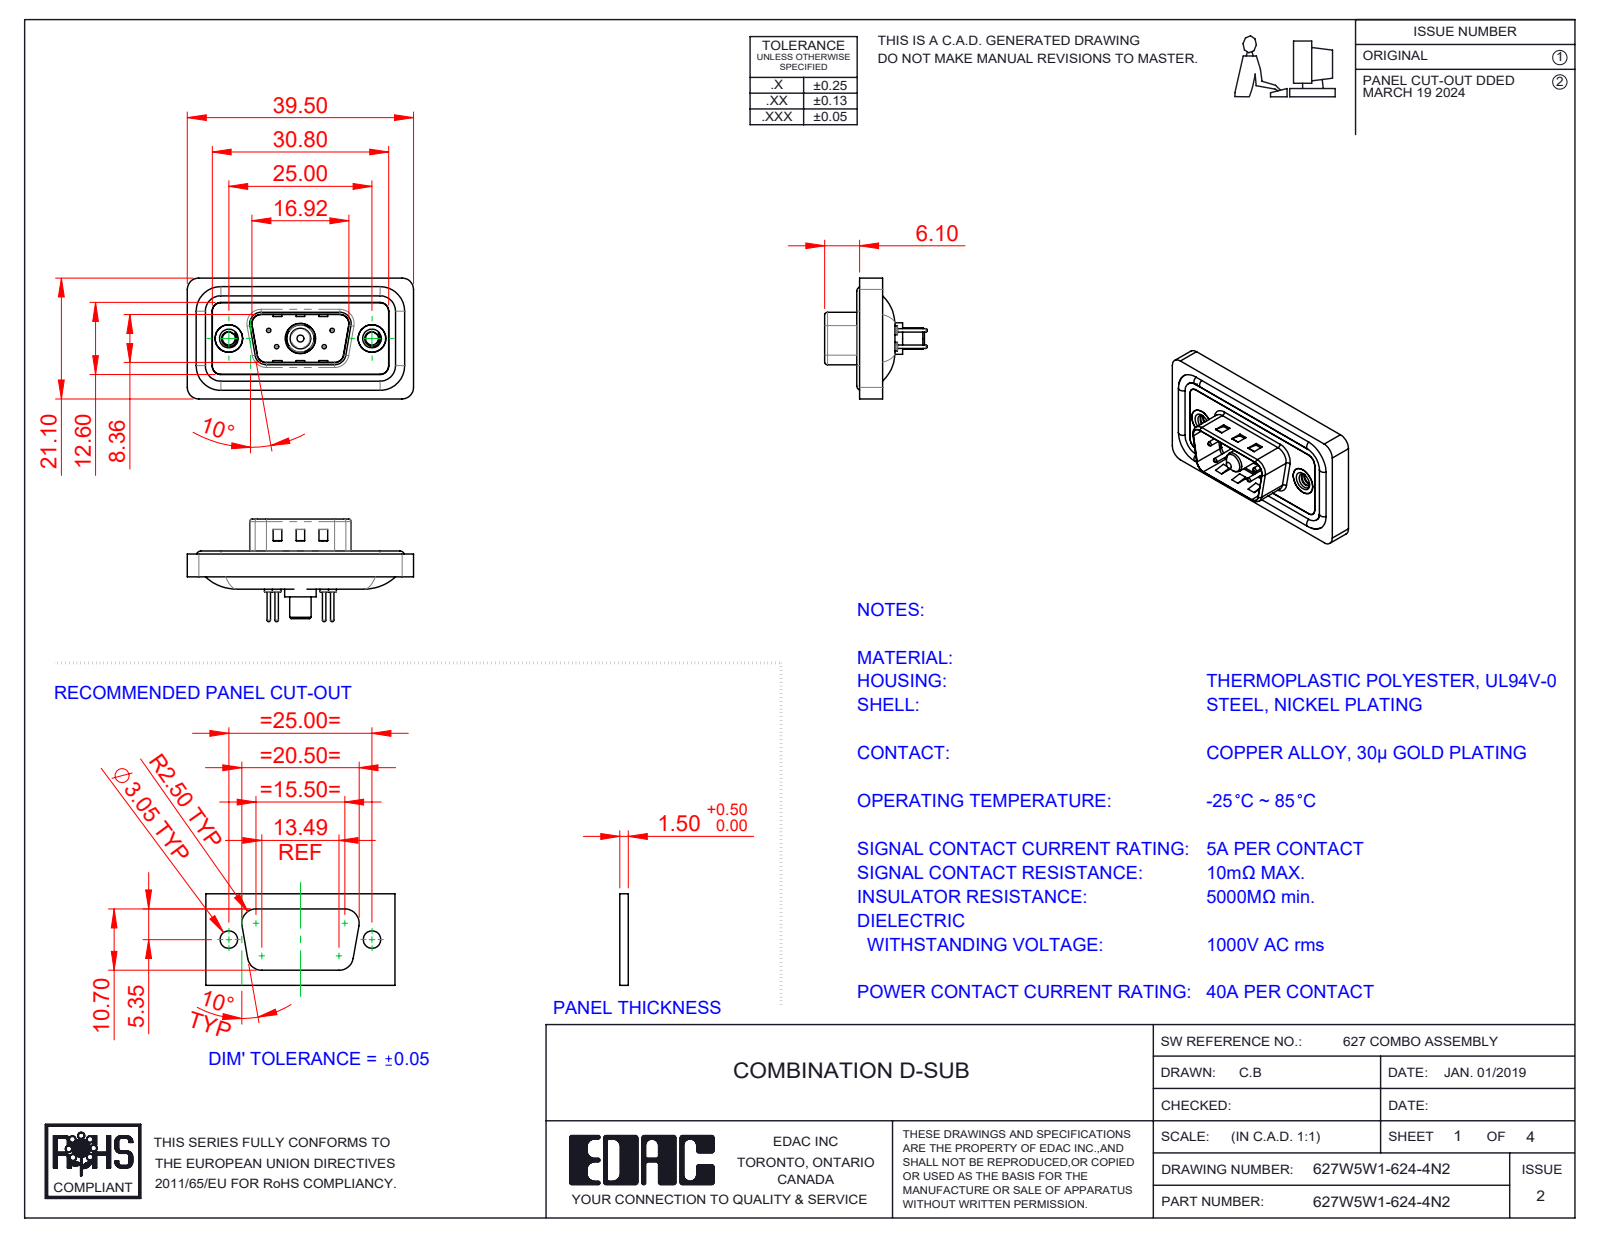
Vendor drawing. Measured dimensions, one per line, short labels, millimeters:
name: 627Combo Waterproof Housing_09 Contacts; 627W5W1-624-4N2; 627Combo Threaded Rivet_2; 627Combo Contact Row 2_24 (+5 more)
written by: SolidWorks 2023 (CONFIG_CONTROL_DESIGN)
unit: mm
bodies: 13 solids, 598 faces (183 planar, 255 cylindrical, 160 other)
size: 39.5 × 21.1 × 17.9
volume: 4 406 mm³; area: 6 952 mm²
holes: 4× ⌀0.75, 4× ⌀1.6, 4× ⌀2, 2× ⌀2.26, 2× ⌀4, 2× ⌀4.8, 2× ⌀5, 1× ⌀4.85, 1× ⌀5.3
bosses: 4× ⌀1.6, 4× ⌀1.5, 4× ⌀0.6, 2× ⌀4.9, 1× ⌀5.5, 1× ⌀5.2, 1× ⌀4.75, 1× ⌀3.75
rounds: 22× R1.5, 18× R2, 8× R0.5, 8× R1.6, 4× R0.25, 4× R0.6, 4× R0.65, 4× R0.9
face distances: 0.4, 1.1, 2.9, 1.6, 3.1, 0.5, 1.5, 2.5, 4, 0.8
hole spacings: 3.16, 5.72, 7.1, 12.5, 18.1, 4.39, 4.4, 8.31
